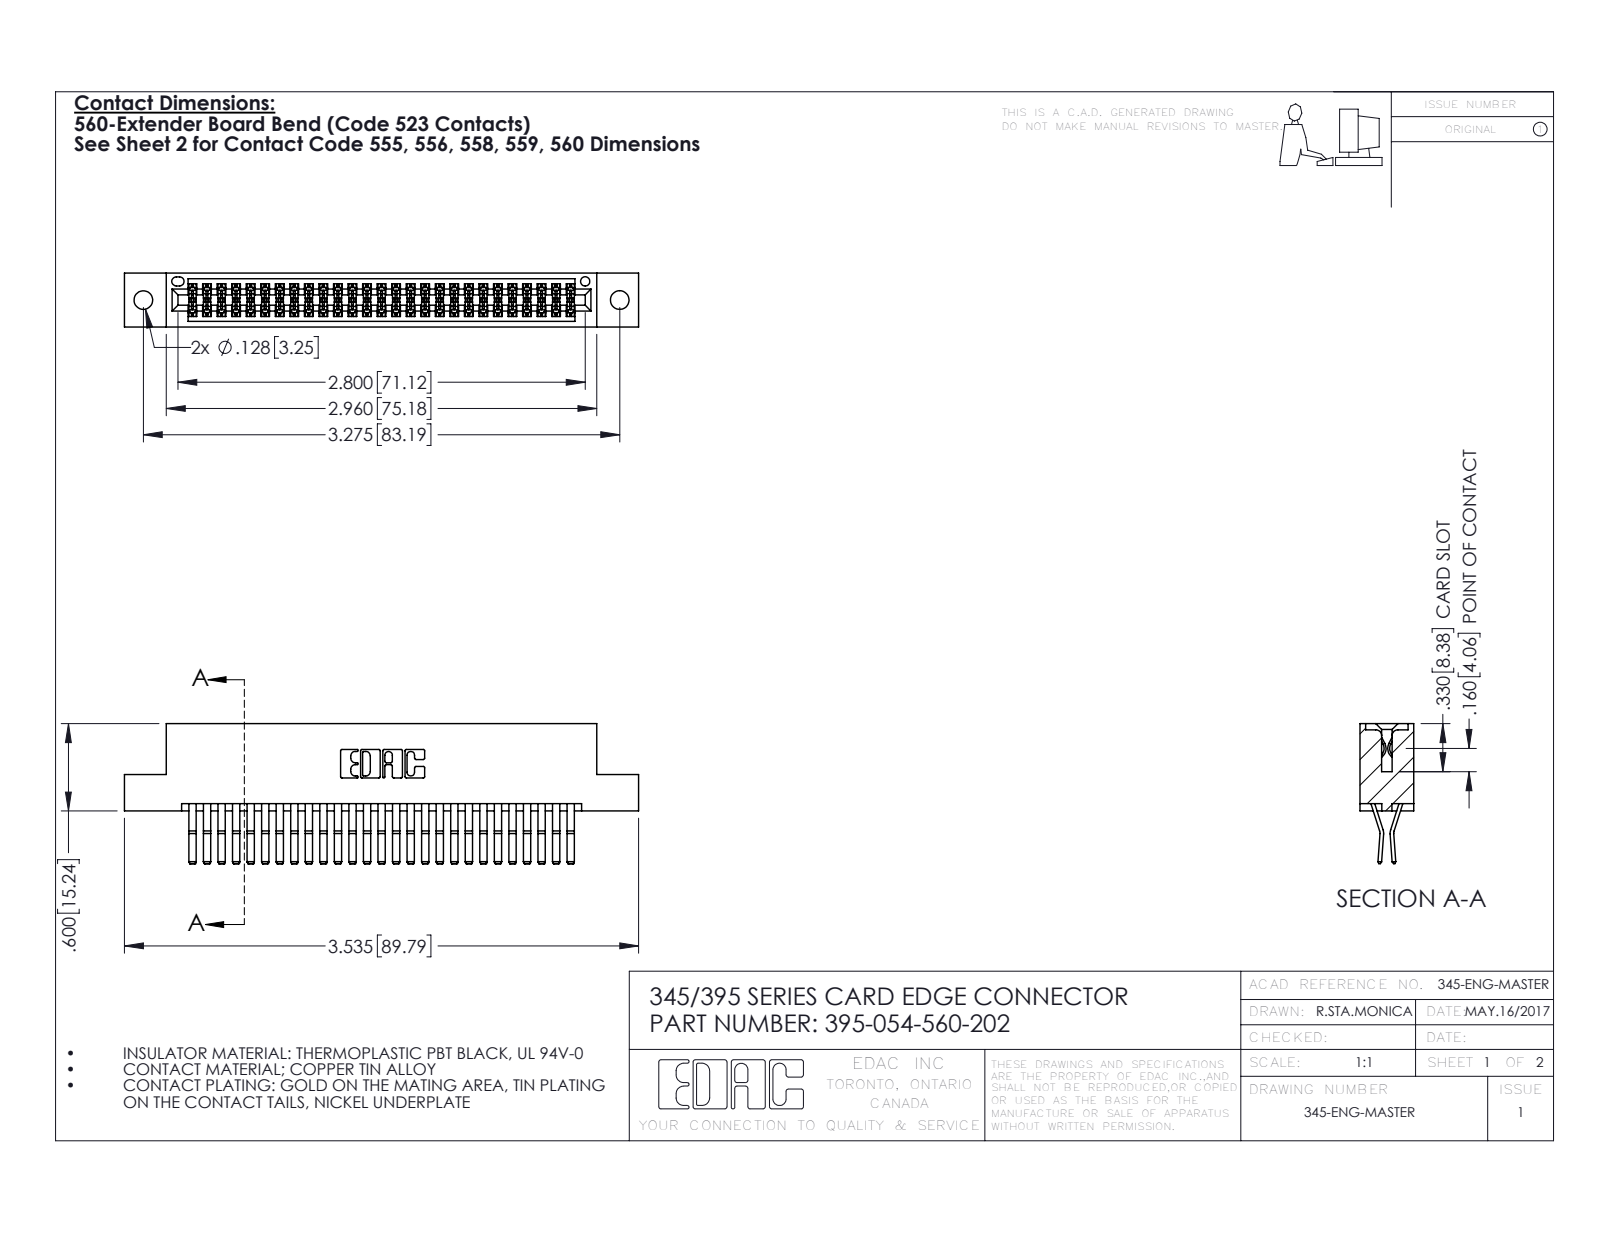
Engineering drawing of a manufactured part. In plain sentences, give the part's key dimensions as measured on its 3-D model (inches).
The part is named "345-292-001_560 Tail; 345 Part_Flush Mounting Lugs - 0.128 Dia; 395-054-560-202". Its 3-D file was written by "SolidWorks 2016 (CONFIG_CONTROL_DESIGN)". It is 55 solids with 2934 faces: 1862 planar, 1072 cylindrical and 0 other. Overall it measures 3.535 by 0.962 by 0.37 inches. Its volume is 0.543 cubic inches and its surface area 20.93 square inches. Round holes: 2 of diameter 0.128, 1 of diameter 0.064. Partial cylindrical surfaces (rounded edges, fillets, slot ends): 81 of radius 0.006, 22 of radius 0.01, 6 of radius 0.007, 6 of radius 0.031, 3 of radius 0.026, 2 of radius 0.01, 2 of radius 0.014, 2 of radius 0.019. The main face-to-face distances are 0.025, 0.298, 0.072, 0.2, 0.37, 0.098, 0.272, 0.225, 0.175, 0.149. The hole center spacings are 0.27, 3.04, 3.275.
